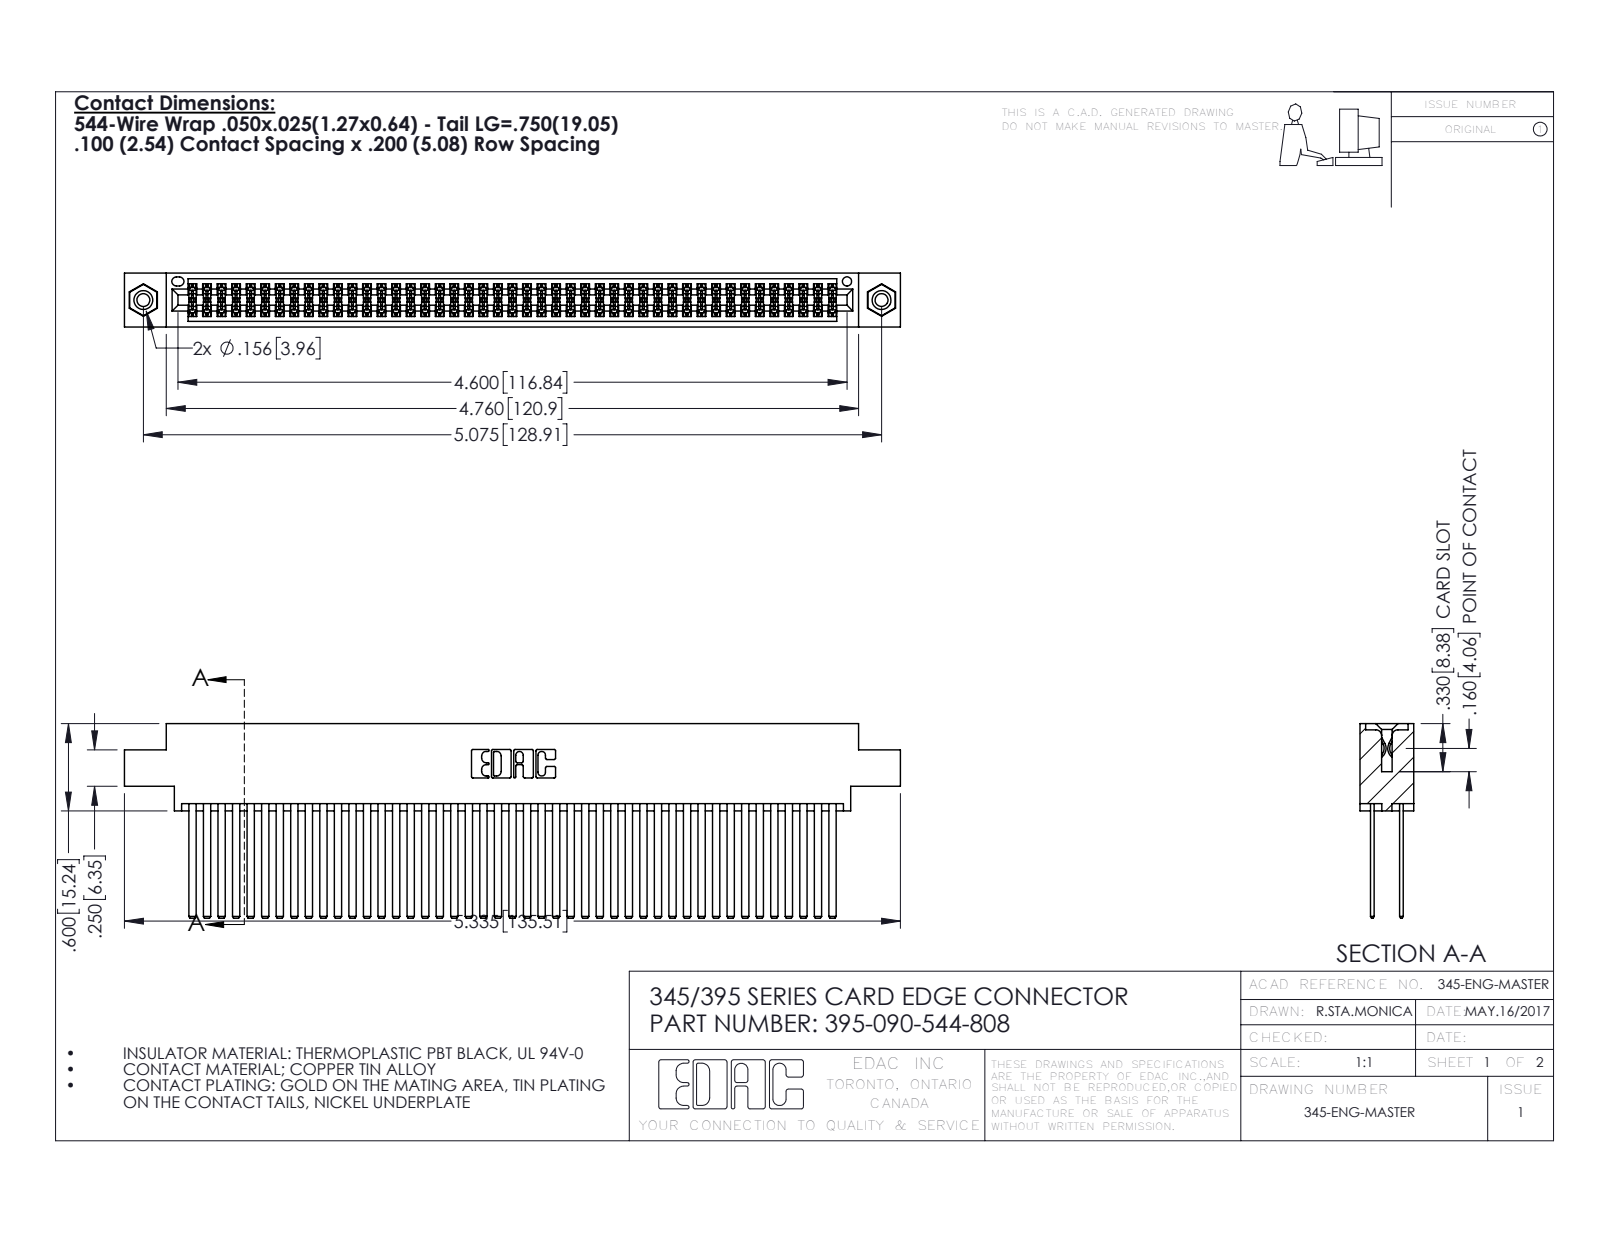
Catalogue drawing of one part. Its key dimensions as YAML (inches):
part_name: "395-090-544-808; 345-292-001_345-293-144; 345 Part_0.170 Offset - 0.156 Dia-TI; 345-250-001_345-250-003-102"
step_written_by: "SolidWorks 2016 (CONFIG_CONTROL_DESIGN)"
units: inches
bodies: {solids: 93, faces: 4150, planar: 2726, cylindrical: 1408, other: 16}
overall_size: [5.335, 1.337, 0.37]
volume: 0.875
surface_area: 38.9
round_holes:
  - {diameter: 0.089, count: 2}
  - {diameter: 0.125, count: 2}
  - {diameter: 0.156, count: 2}
  - {diameter: 0.064, count: 1}
round_bosses_or_shafts:
  - {diameter: 0.155, count: 2}
partial_cylinders:
  - {radius: 0.006, count: 135}
  - {radius: 0.01, count: 22}
  - {radius: 0.007, count: 6}
  - {radius: 0.031, count: 6}
  - {radius: 0.026, count: 3}
  - {radius: 0.014, count: 2}
  - {radius: 0.019, count: 2}
  - {radius: 0.022, count: 2}
face_to_face_distances: [0.2, 0.025, 0.072, 0.098, 0.272, 0.298, 0.225, 0.175, 0.37, 0.15]
hole_center_spacings: [0.27, 4.839, 5.075]
